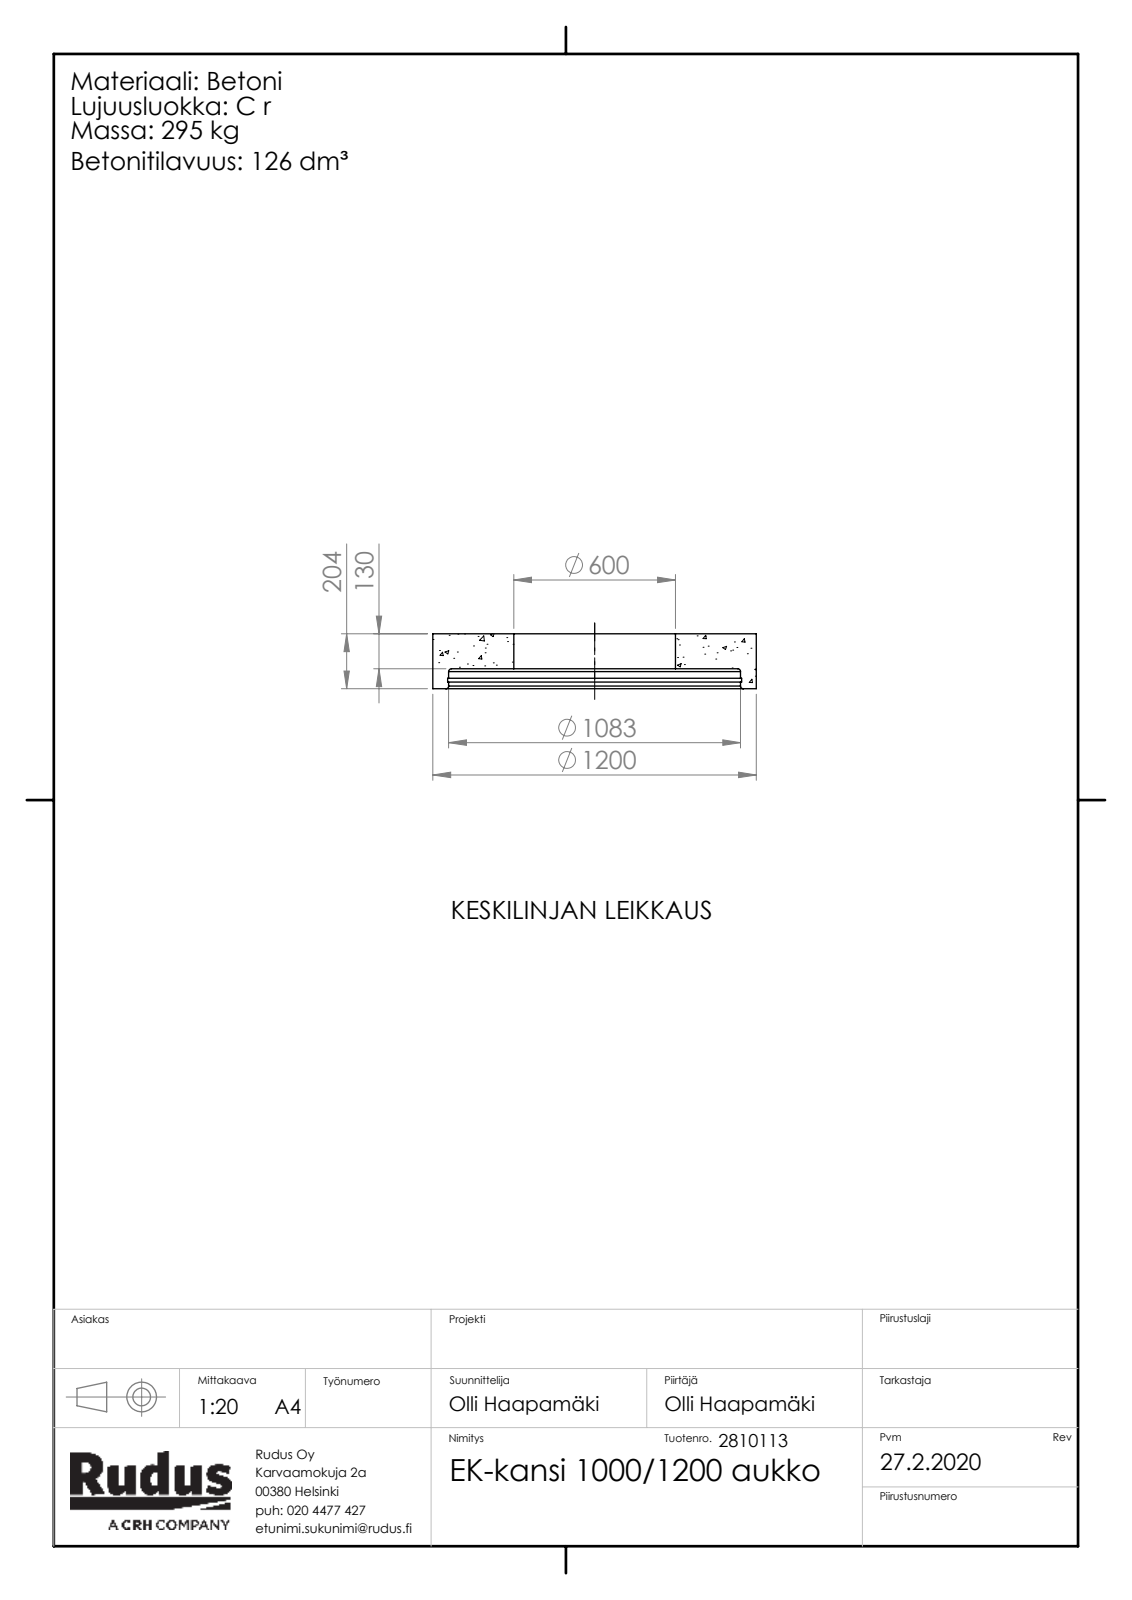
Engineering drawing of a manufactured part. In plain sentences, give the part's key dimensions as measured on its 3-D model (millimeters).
The part is named "EK-osa-kansi_Aukko; Rudus 2810113 EK-kansi 1000_1200 aukko". Its 3-D file was written by "SolidWorks 2019 (CONFIG_CONTROL_DESIGN)". It is 1 solid with 96 faces: 5 planar, 17 cylindrical and 74 other. Overall it measures 1200 by 1200 by 204 millimeters. Its volume is 125 500 000 cubic millimeters and its surface area 2 965 000 square millimeters. Round holes: 1 of diameter 600, 1 of diameter 1083, 1 of diameter 1091. Round bosses or shafts: 1 of diameter 1200. Partial cylindrical surfaces (rounded edges, fillets, slot ends): 1 of radius 597. The main face-to-face distances are 130, 74, 204, 25, 39, 14, 49, 179, 35, 165.
